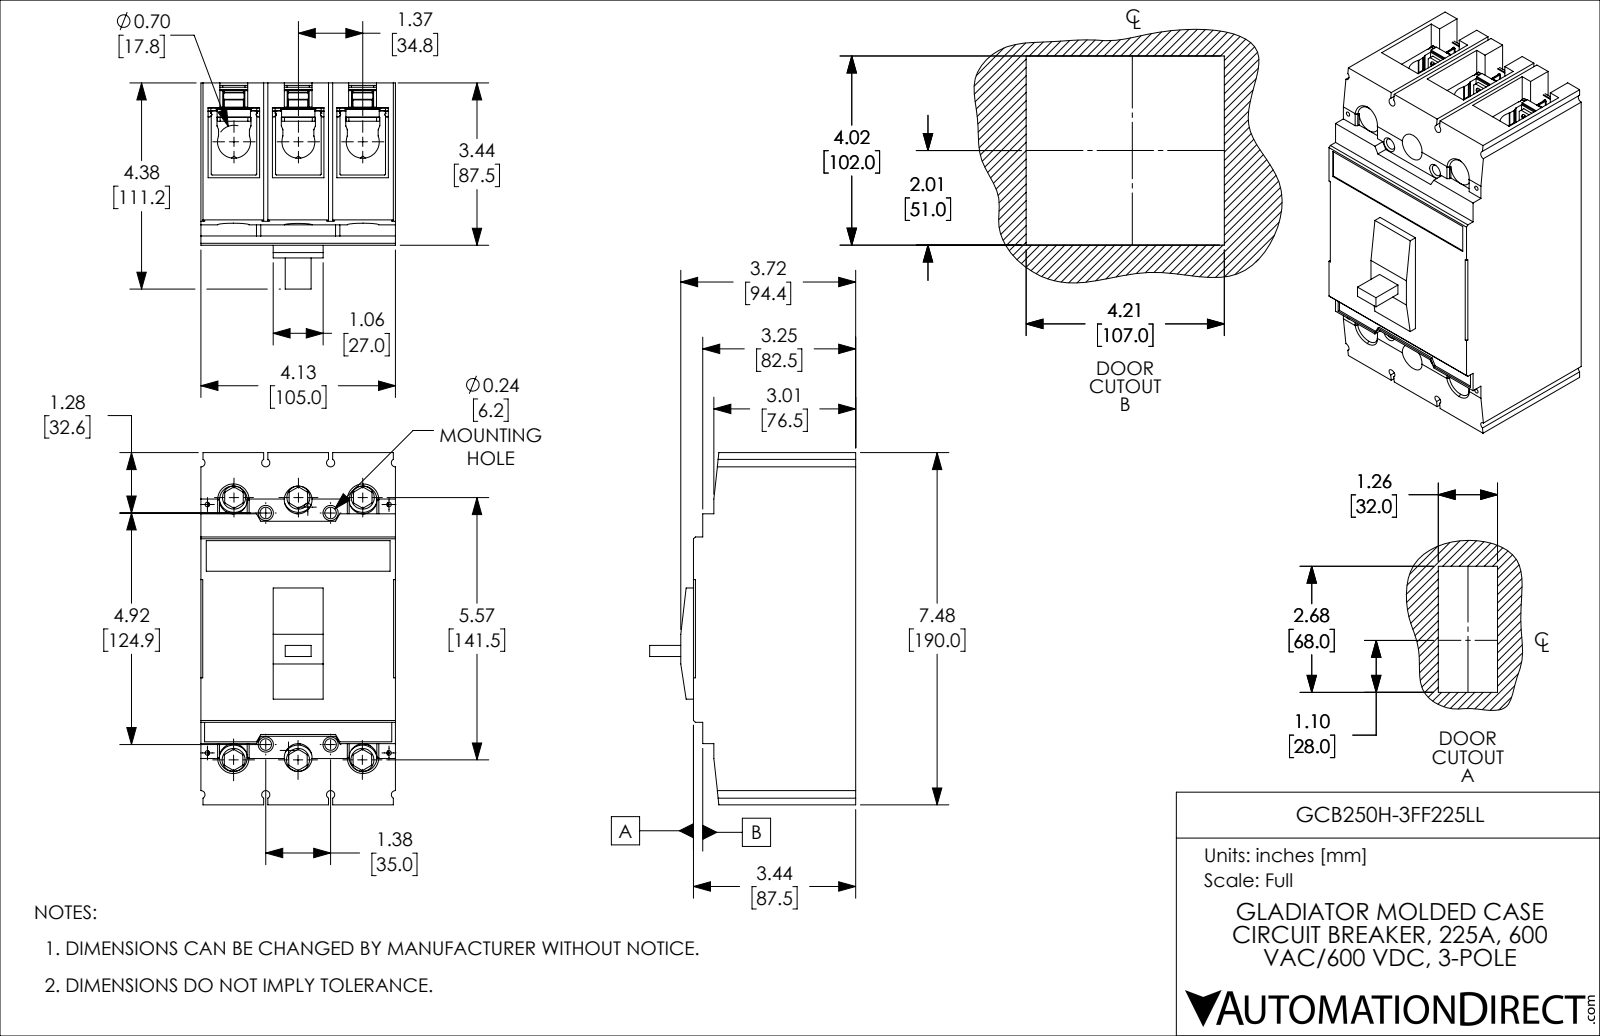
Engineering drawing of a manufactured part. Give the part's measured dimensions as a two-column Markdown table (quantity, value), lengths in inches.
| quantity | value |
| --- | --- |
| part name | GCB250H-3FF225LL |
| STEP written by | SolidWorks 2021 (CONFIG_CONTROL_DESIGN) |
| units | inches |
| bodies | 25 solids, 2233 faces (975 planar, 958 cylindrical, 300 other) |
| overall size | 7.48 × 4.378 × 4.134 |
| volume | 87.11 in³ |
| surface area | 315.7 in² |
| round holes (diameter × count) | 0.067 × 24, 0.157 × 24, 0.098 × 10, 0.354 × 6, 0.591 × 6, 0.689 × 6, 0.173 × 4, 0.244 × 4 |
| round bosses / shafts (diameter × count) | 0.709 × 6 |
| partial cylindrical surfaces (radius × count) | 0.012 × 206, 0.039 × 72, 0.059 × 36, 0.02 × 26, 0.008 × 24, 0.079 × 20, 0.016 × 12, 0.031 × 12 |
| main face-to-face distances | 1.368, 4.134, 2.736, 1.094, 0.843, 0.252, 0.059, 1.378, 6.102, 3.445 |
| hole center spacings | 0.285, 0.743, 1.046, 1.378, 5.24, 6.298, 1.368, 1.426 |
